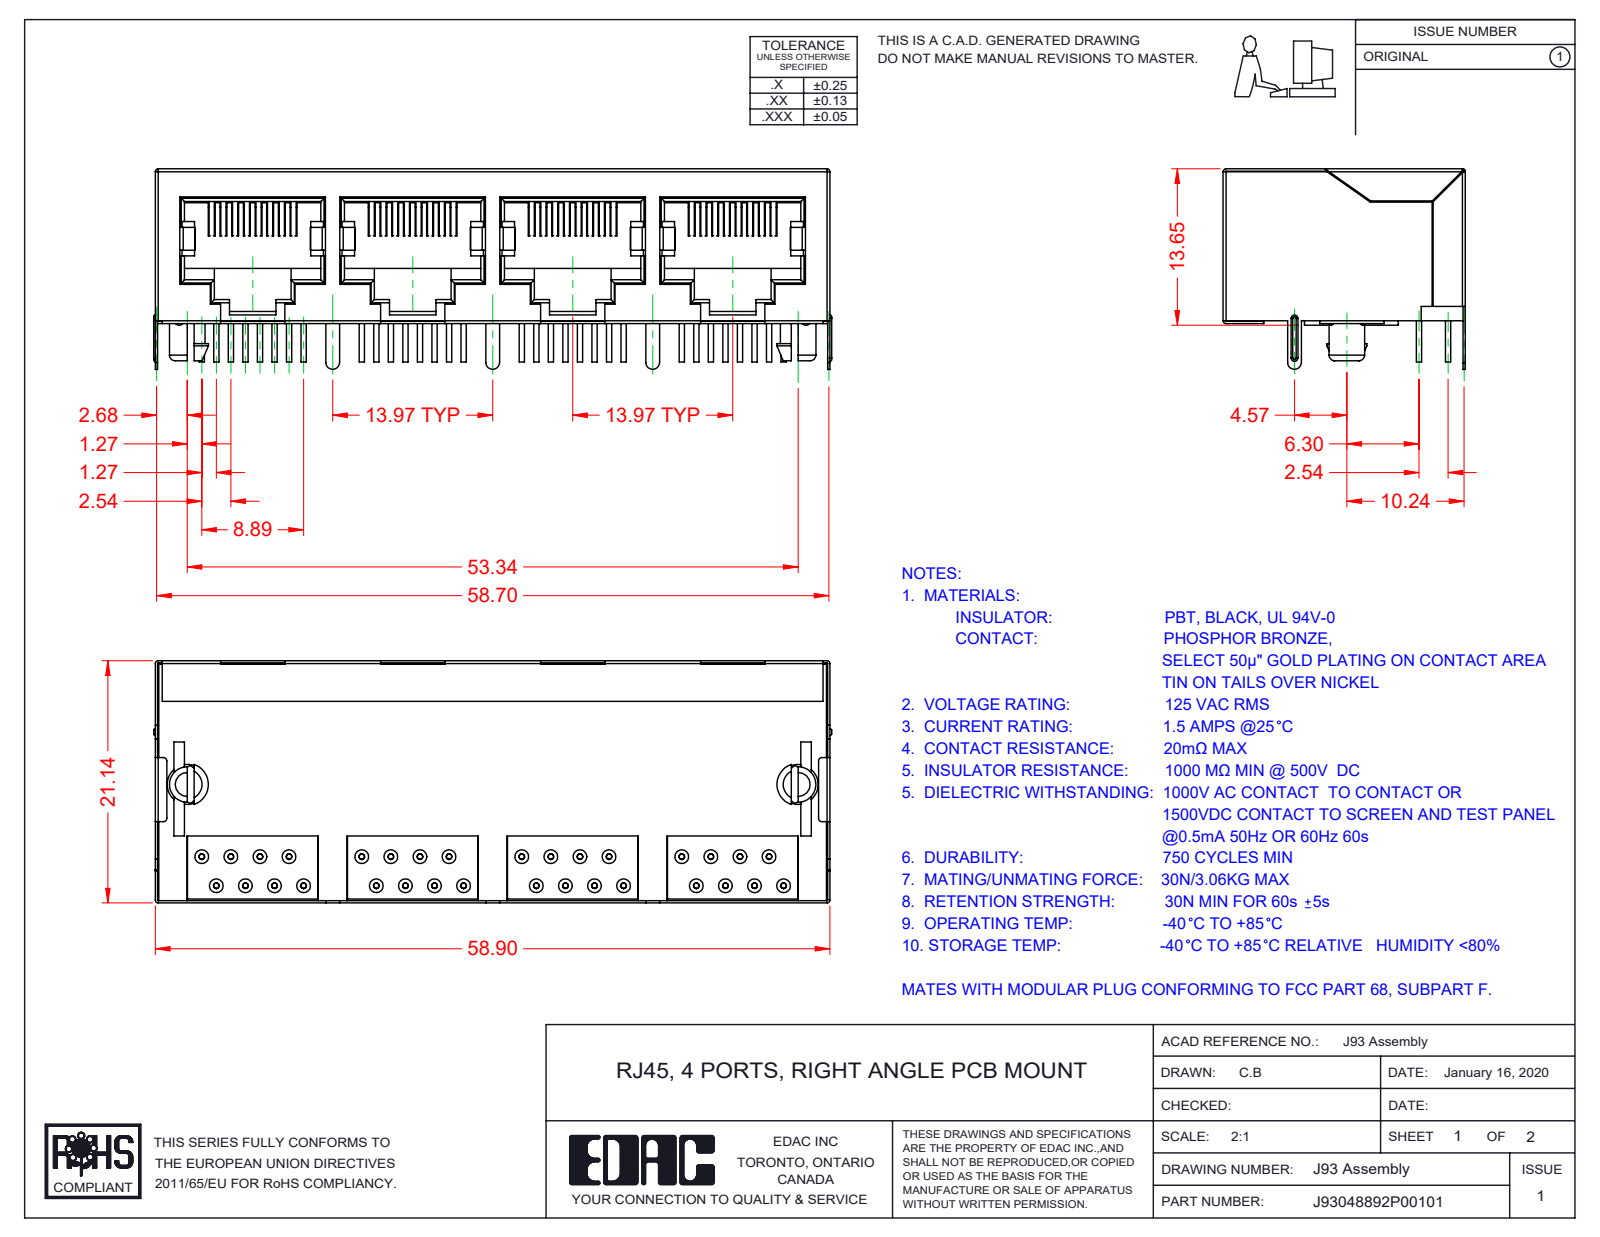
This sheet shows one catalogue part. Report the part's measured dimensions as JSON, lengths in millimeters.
{"part_name": "RJ93048892P00101; 93 Contacts; 93 Shield; 93 Contact Lock (+1 more)", "step_written_by": "SolidWorks 2016 (CONFIG_CONTROL_DESIGN)", "units": "millimeters", "bodies": {"solids": 38, "faces": 2070, "planar": 1065, "cylindrical": 665, "other": 340}, "overall_size": [59.2, 21.14, 17.5], "volume_mm3": 9684, "surface_area_mm2": 21056, "round_holes": [[0.46, 32]], "round_bosses_or_shafts": [[0.46, 128], [3.1, 2]], "partial_cylinders_radius": [[0.3, 22], [0.5, 22], [0.19, 16], [0.25, 11], [0.15, 4], [0.6, 4], [0.4, 2], [0.46, 2]], "face_to_face_distances": [0.8, 12.25, 12.2, 1, 0.75, 13.25, 13.05, 1.05, 0.85, 13], "hole_center_spacings": [2.84, 2.54, 13.97, 15.45, 12.95, 4.58, 16.51, 11.43]}
